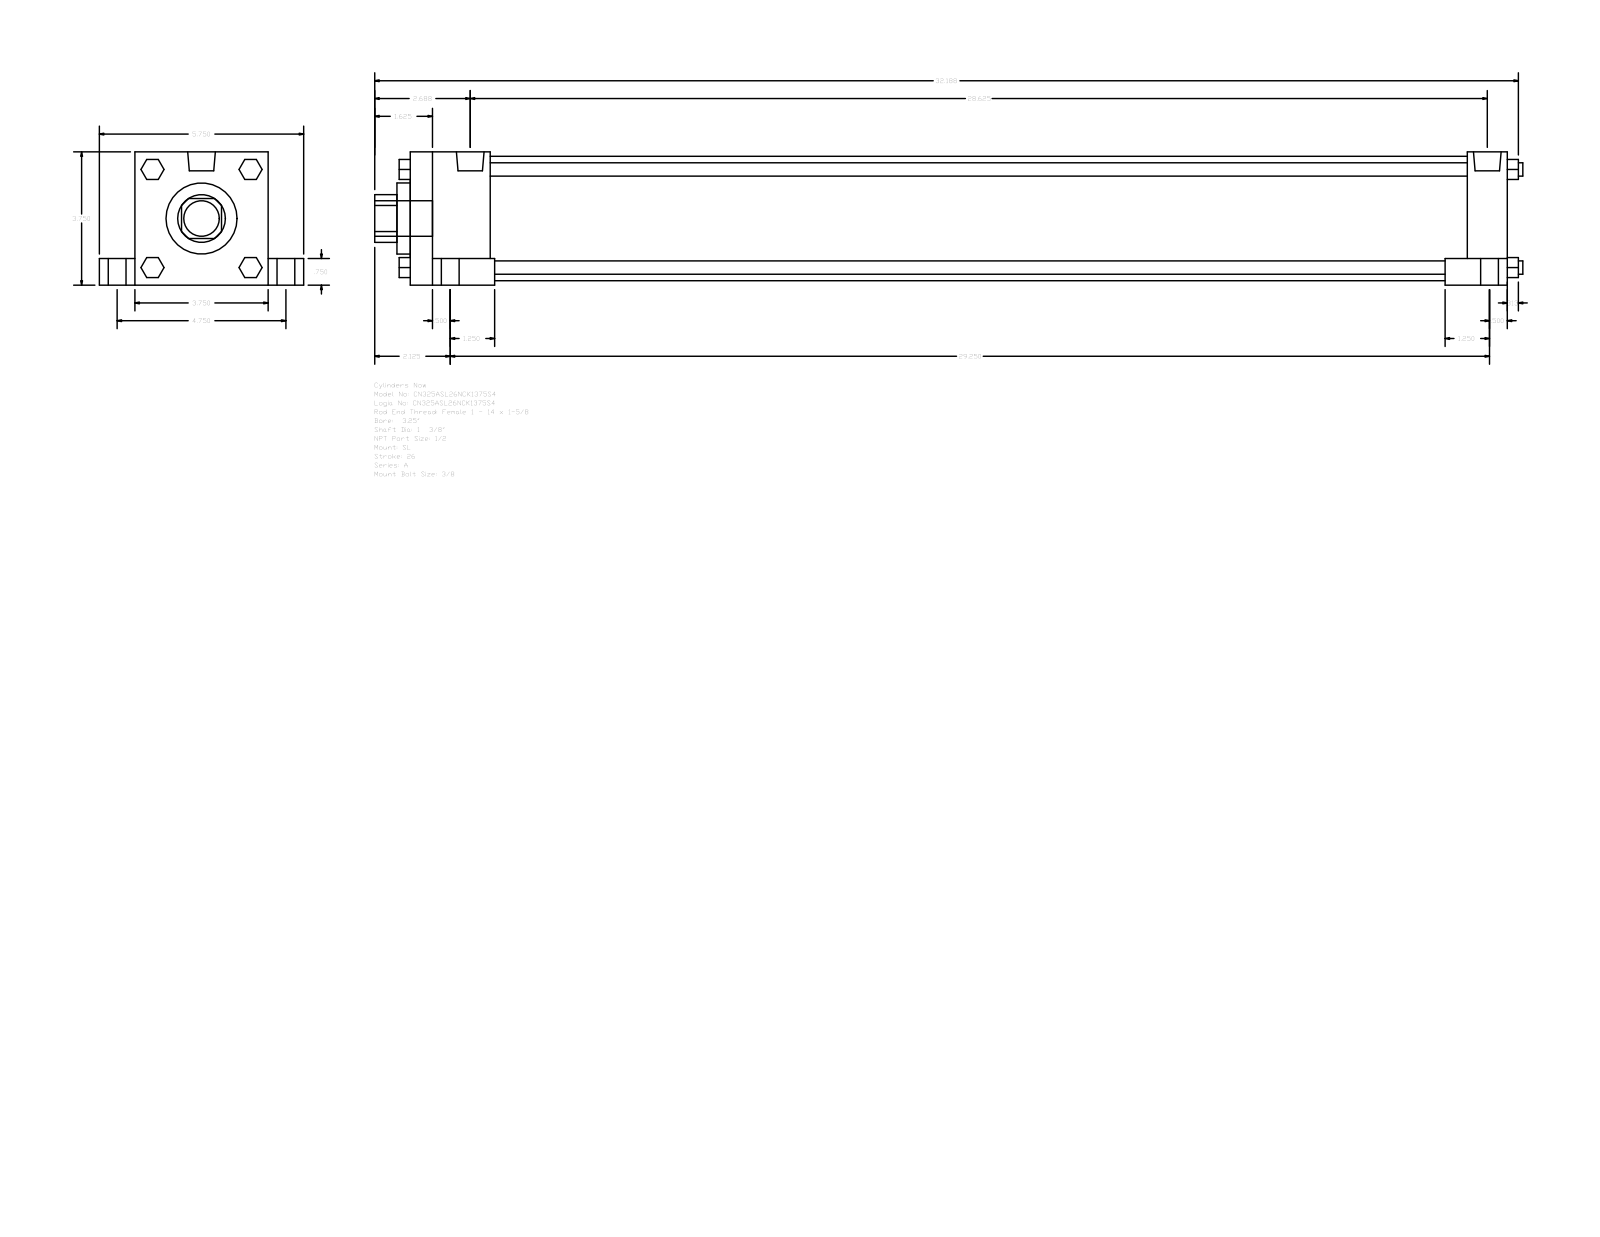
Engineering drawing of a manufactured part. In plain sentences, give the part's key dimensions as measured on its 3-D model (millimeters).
The part is named "A_SL__0325_1.375". Its 3-D file was written by "GSSL Pune (CONFIG_CONTROL_DESIGN)". It is 0 solids with 150 faces: 114 planar, 36 cylindrical and 0 other. Overall it measures 820.74 by 146.05 by 95.25 millimeters. Round holes: 1 of diameter 34.92, 1 of diameter 50.8, 1 of diameter 88.9. Round bosses or shafts: 4 of diameter 19.05, 4 of diameter 12.7, 4 of diameter 9.53, 4 of diameter 8.73, 2 of diameter 19.77, 1 of diameter 25.4. Partial cylindrical surfaces (rounded edges, fillets, slot ends): 1 of radius 17.06. The main face-to-face distances are 95.24, 784.22, 25.41, 120.65, 19.05, 76.19, 28.57, 57.15, 755.65, 698.5.
